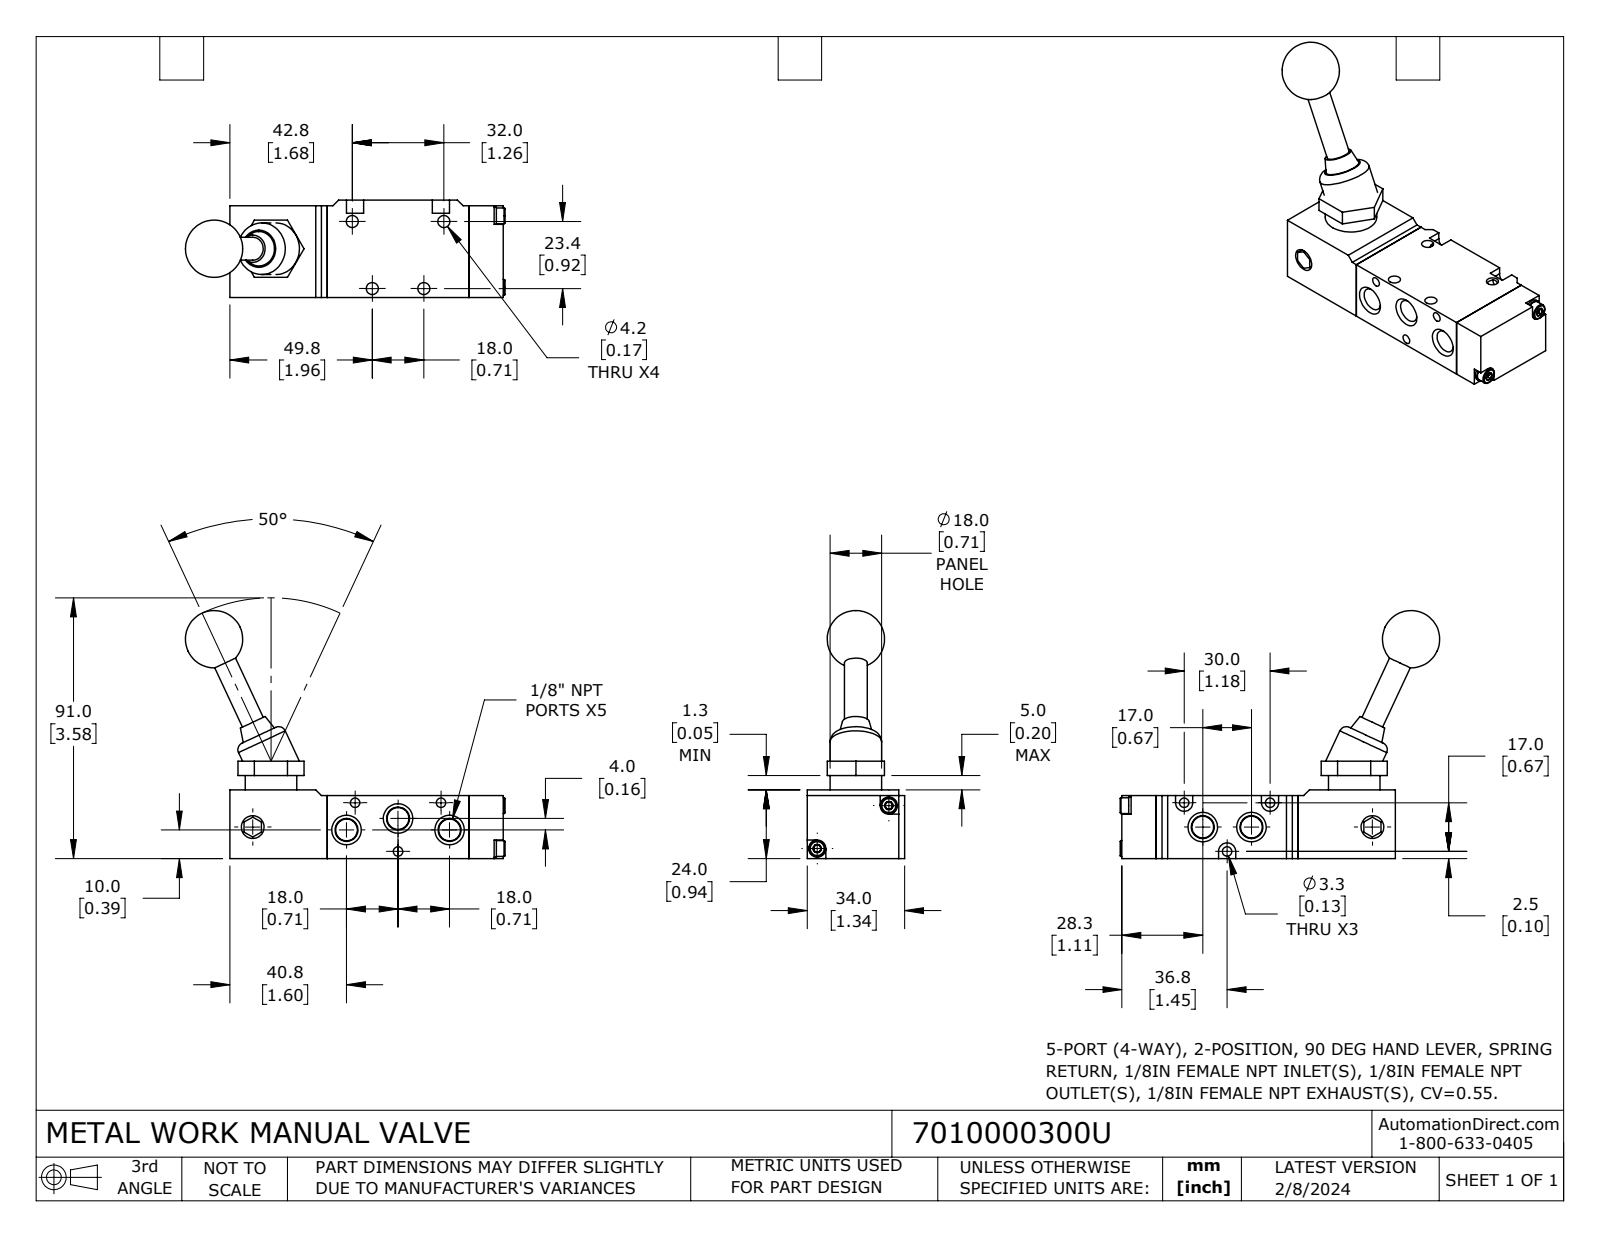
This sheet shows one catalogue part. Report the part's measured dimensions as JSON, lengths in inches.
{"part_name": "7010000300U", "step_written_by": "SolidWorks 2023 (CONFIG_CONTROL_DESIGN)", "units": "inches", "bodies": {"solids": 8, "faces": 208, "planar": 105, "cylindrical": 49, "other": 54}, "overall_size": [4.393, 3.409, 1.339], "volume_in3": 4.828, "surface_area_in2": 34.88, "round_holes": [[0.165, 4], [0.13, 3], [0.118, 2], [0.313, 1]], "round_bosses_or_shafts": [[0.709, 2], [0.236, 2], [0.217, 2], [0.315, 1]], "partial_cylinders_radius": [[0.118, 3]], "face_to_face_distances": [0.866, 1.339, 1.949, 0.079, 1.26, 0.472, 3.287, 0.945, 2.421, 3.76], "hole_center_spacings": [0.893, 0.961, 1.348, 0.709, 1.148, 1.181, 1.26, 1.447]}
